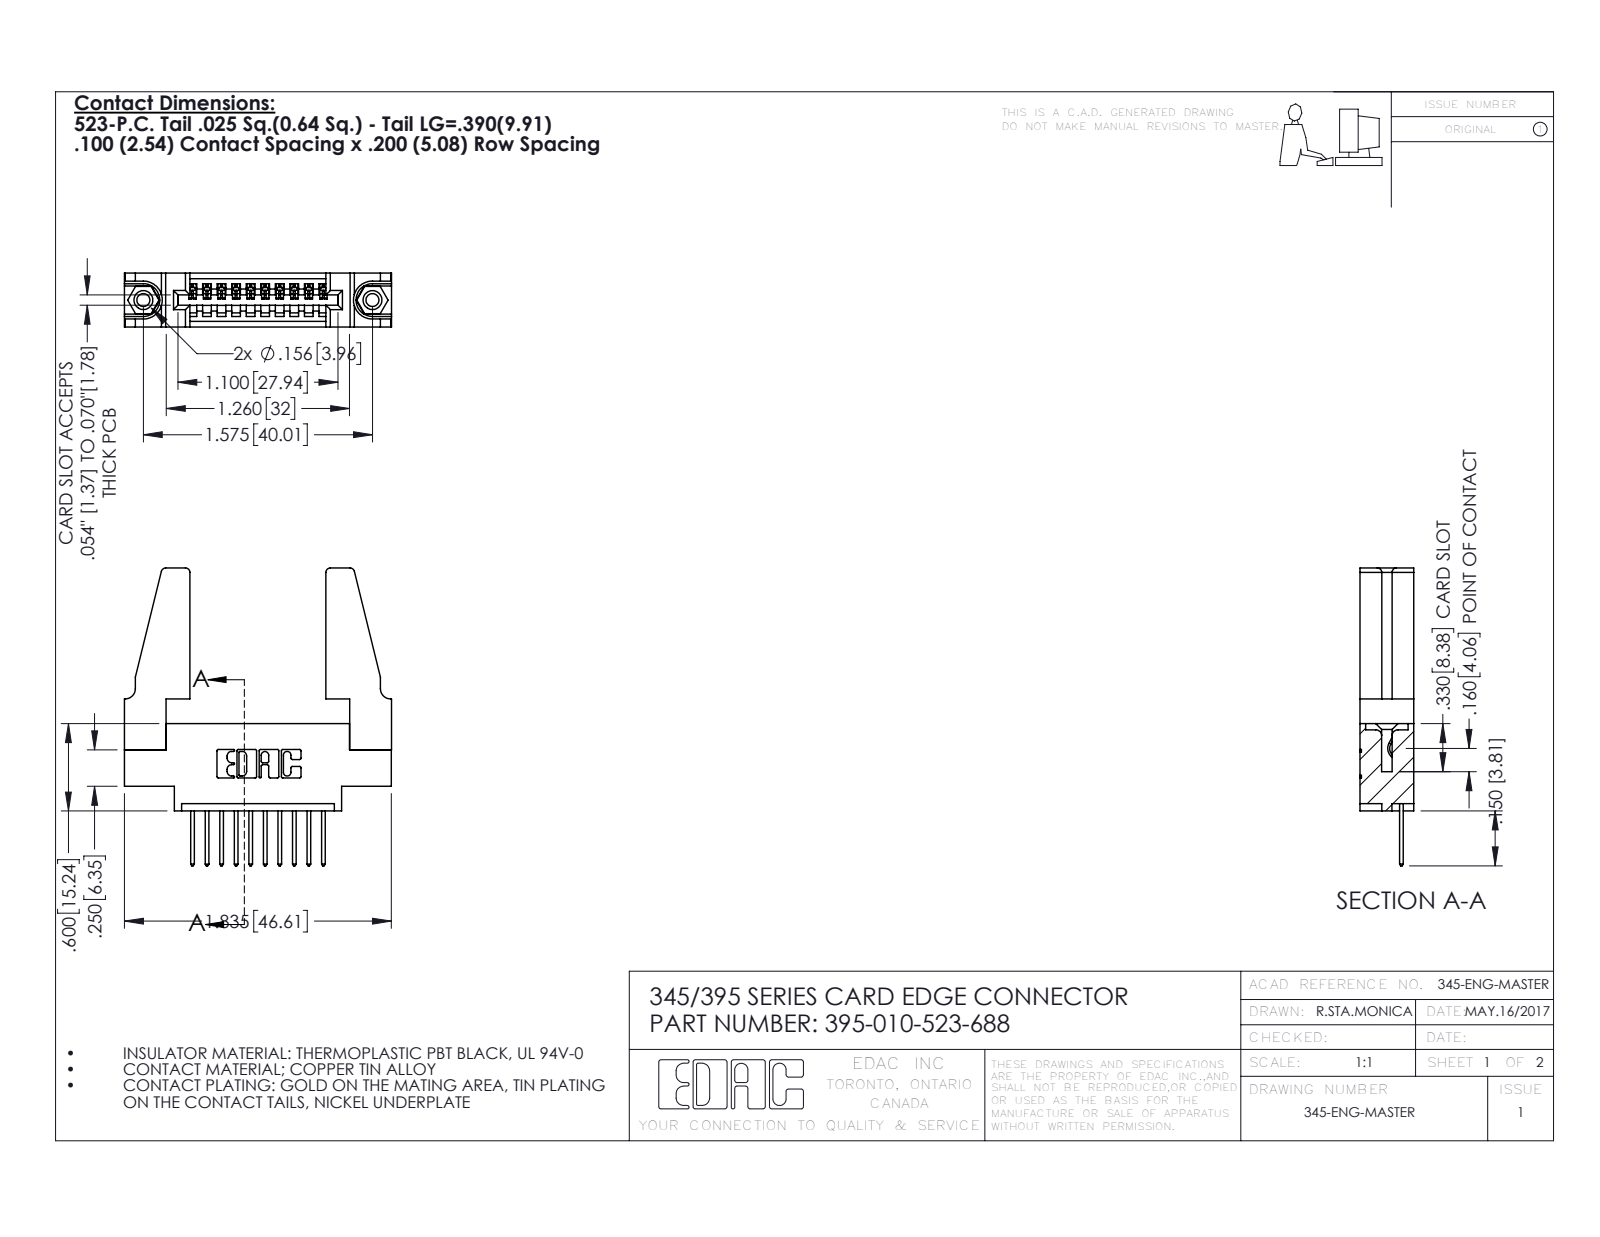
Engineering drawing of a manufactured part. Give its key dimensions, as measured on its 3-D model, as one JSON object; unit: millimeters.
{"part_name": "345-250-001_345-250-001-102; 395-010-523-688; 345-292-001_345-293-123; 345 Part_0.170 Offset - 0.156 Dia-TH (+1 more)", "step_written_by": "SolidWorks 2016 (CONFIG_CONTROL_DESIGN)", "units": "millimeters", "bodies": {"solids": 15, "faces": 834, "planar": 556, "cylindrical": 262, "other": 16}, "overall_size": [52, 46.6, 9.4], "volume_mm3": 7310, "surface_area_mm2": 8213, "round_holes": [[2.3, 2], [3.2, 2], [4, 2], [1.6, 1]], "round_bosses_or_shafts": [[3.9, 2]], "partial_cylinders_radius": [[0.3, 22], [0.2, 20], [0.3, 20], [0.8, 8], [0.2, 6], [0.8, 6], [0.7, 3], [0.8, 2]], "face_to_face_distances": [9.4, 1.8, 7.6, 5.1, 2.5, 6.9, 0.6, 3.8, 3.8, 5.7], "hole_center_spacings": [6.9, 34.1, 40]}
